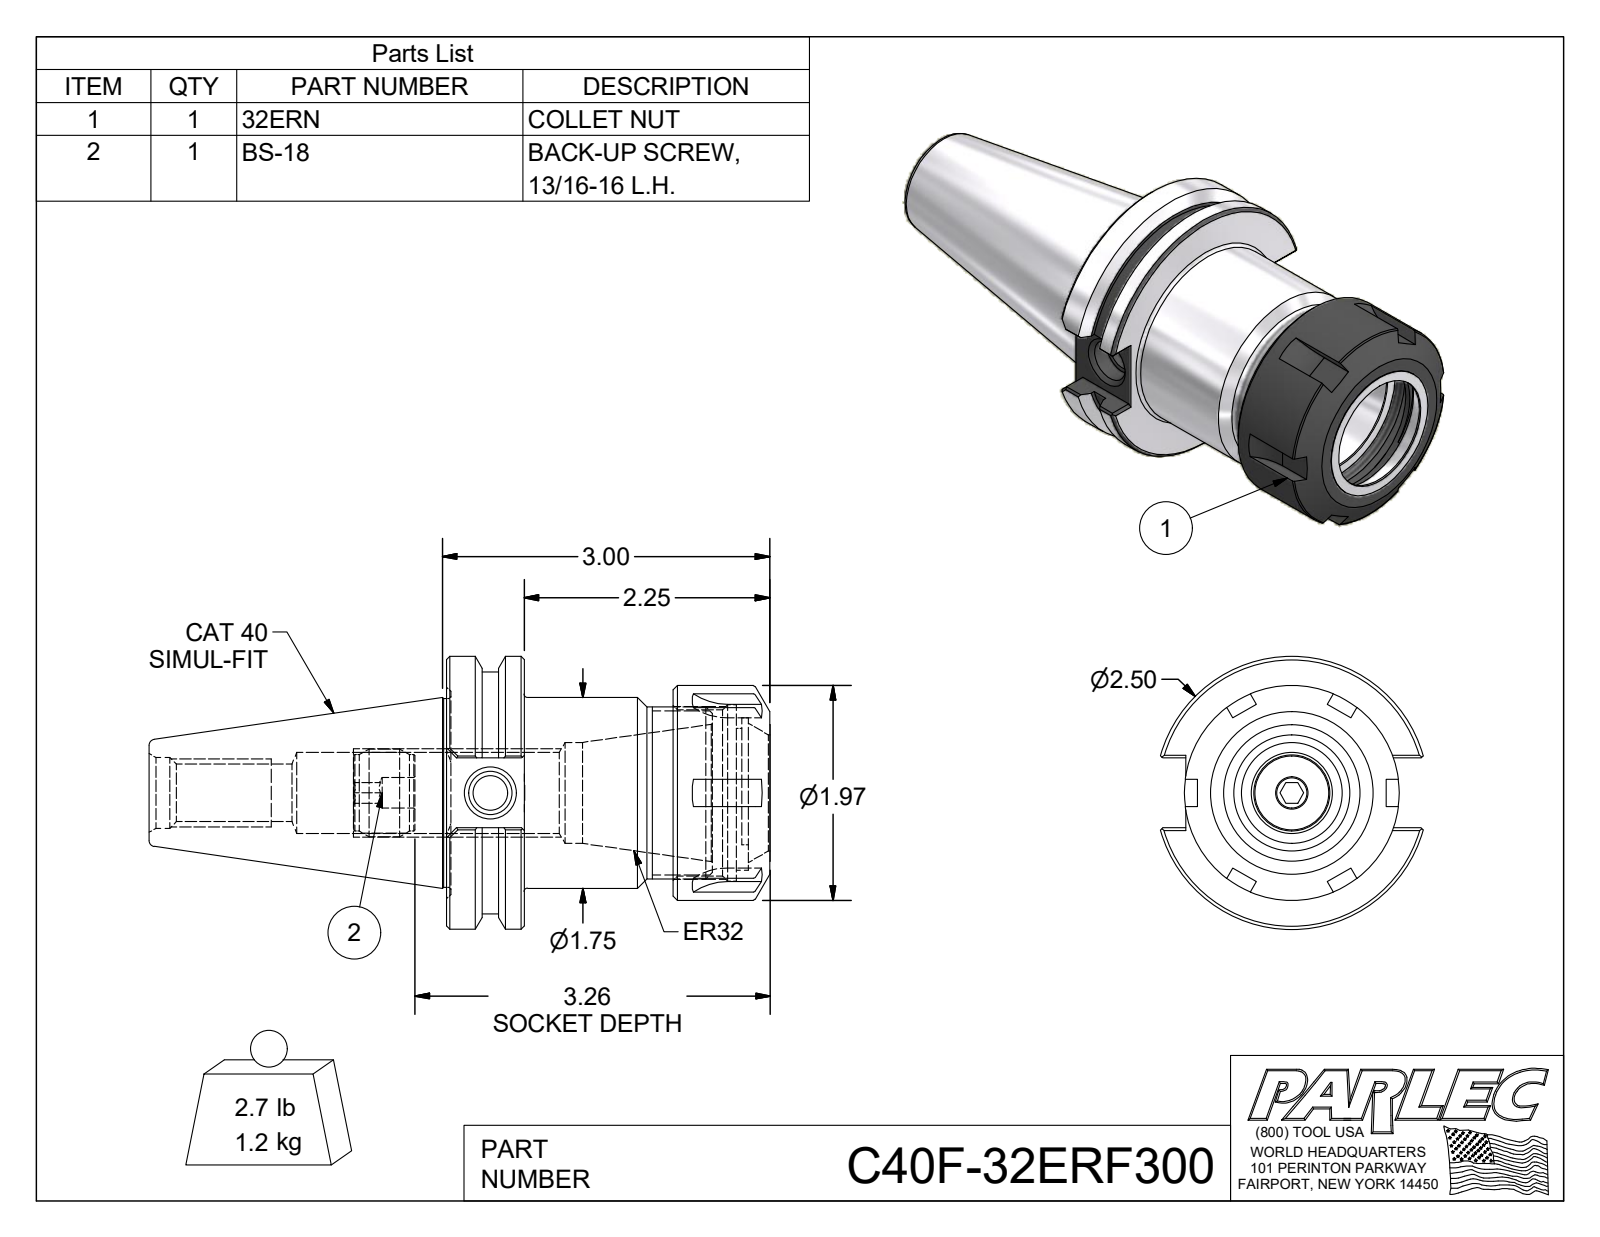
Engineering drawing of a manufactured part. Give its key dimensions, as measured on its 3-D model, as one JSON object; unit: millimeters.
{"part_name": "C40F-32ER3-1; 32ERN; BS-18; C40F-32ERF300", "step_written_by": "Autodesk Inventor 2016 (AUTOMOTIVE_DESIGN)", "units": "millimeters", "bodies": {"solids": 3, "faces": 175, "planar": 74, "cylindrical": 37, "other": 64}, "overall_size": [144.46, 63.5, 61.11], "volume_mm3": 157645, "surface_area_mm2": 40559, "round_holes": [[7.11, 1], [8, 1], [10.13, 1], [13.39, 1], [16.46, 1], [18.92, 1], [23.5, 1], [27, 1], [33.02, 1], [38.65, 1], [41, 1]], "round_bosses_or_shafts": [[63.5, 1], [56.26, 1], [50, 1], [44.45, 1], [40, 1], [20.45, 1], [17.78, 1]], "partial_cylinders_radius": [[0.51, 12], [14.9, 1], [17.5, 1]], "face_to_face_distances": [18.04, 52.41, 75.19, 57.15, 34.37, 22.78, 67.42, 49.38, 15.01, 7.77], "hole_center_spacings": [1.86]}
